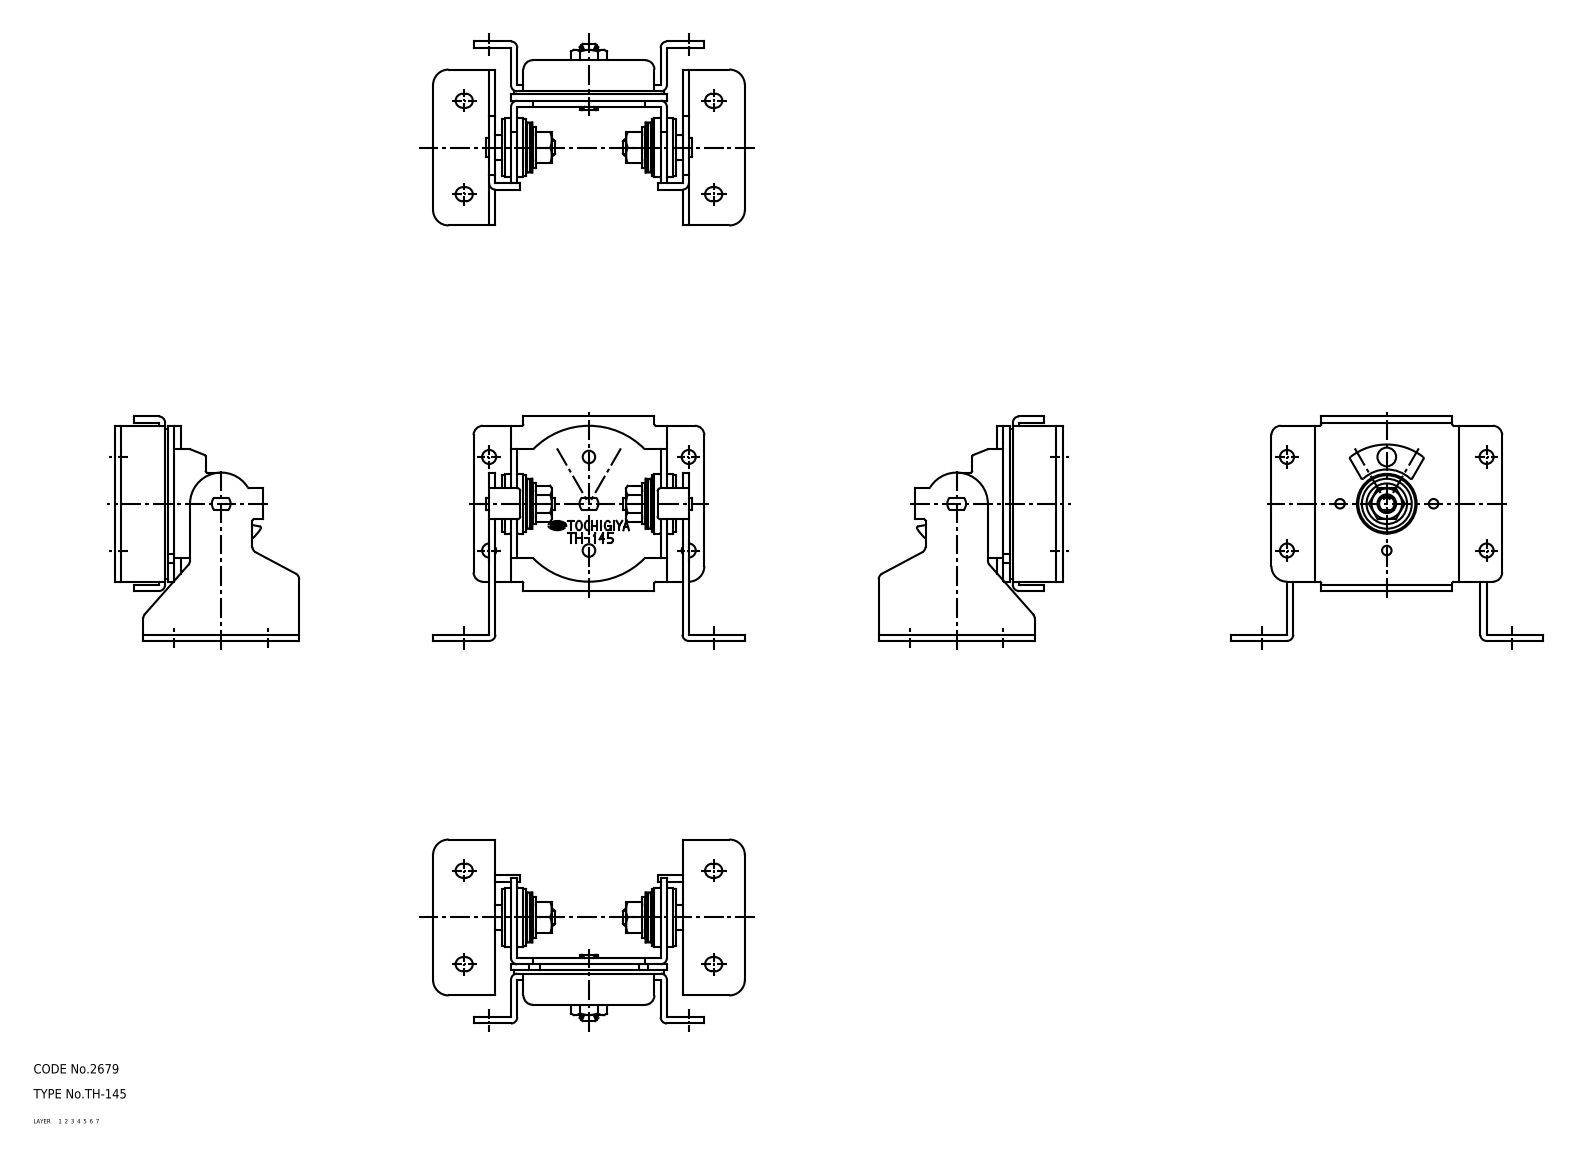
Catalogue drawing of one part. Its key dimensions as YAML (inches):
part_name: "tray; disk; washer_A; washer_B (+8 more)"
step_written_by: "CADfix (AUTOMOTIVE_DESIGN)"
units: inches
bodies: {solids: 32, faces: 496, planar: 0, cylindrical: 0, other: 496}
overall_size: [3.937, 2.835, 2.323]
volume: 2.485
surface_area: 78.2
